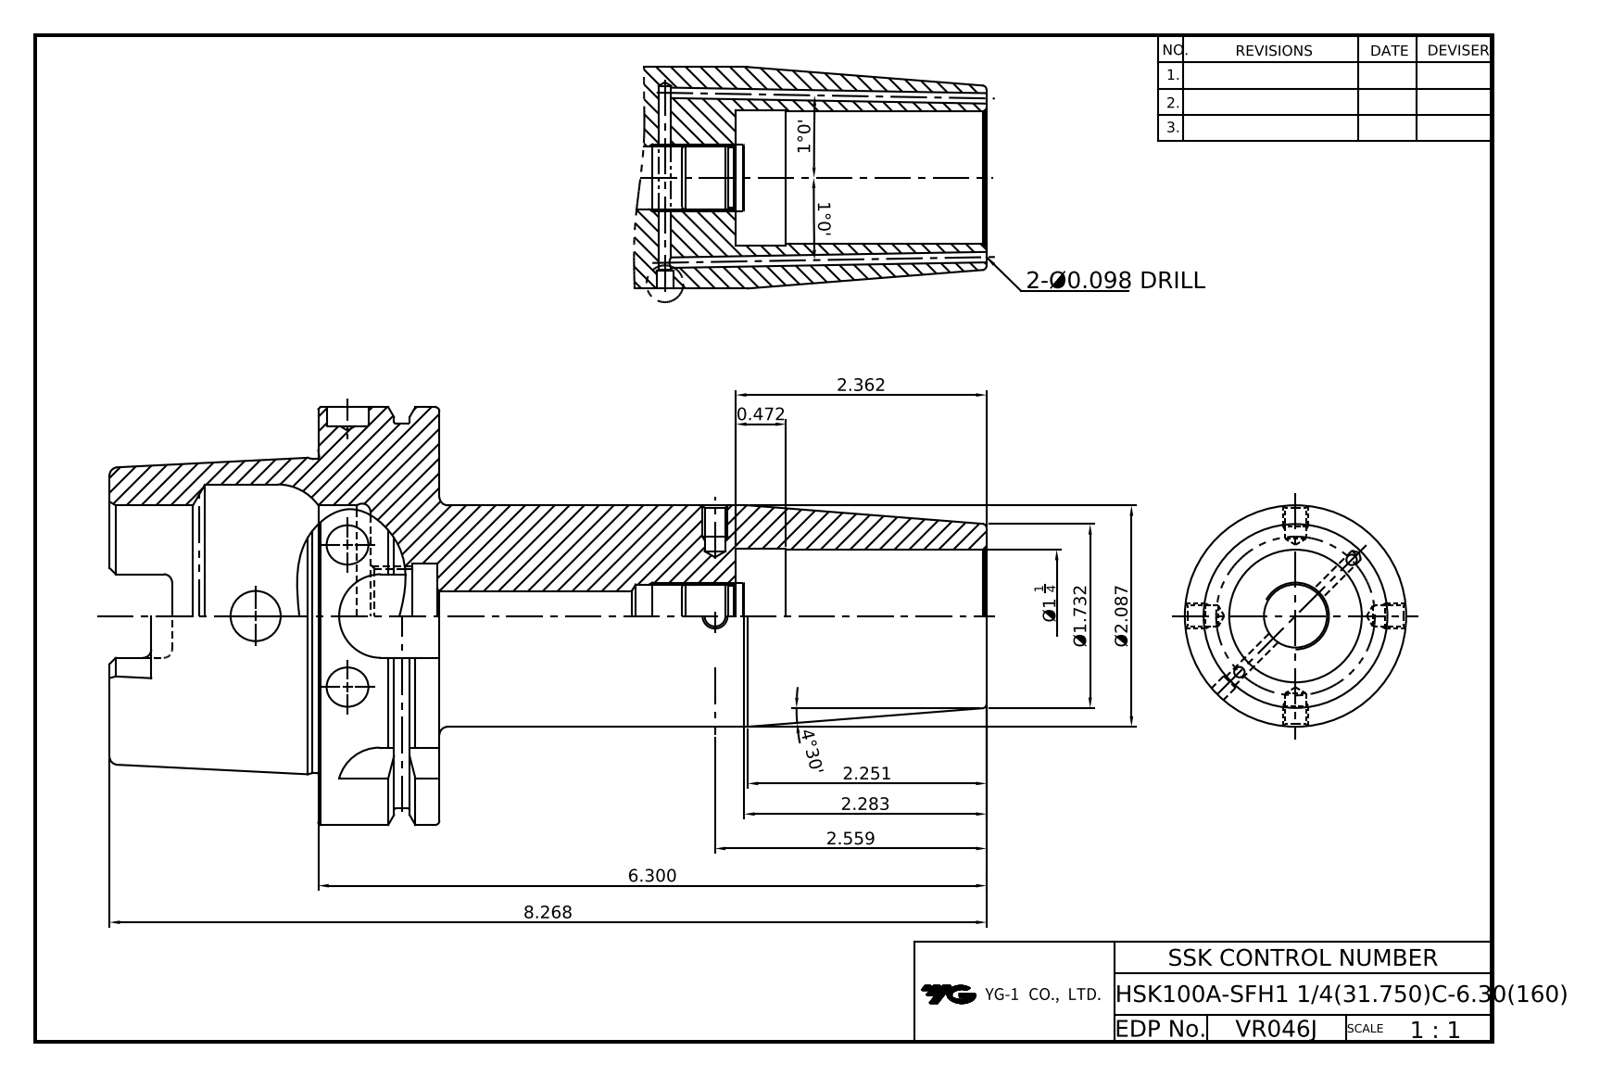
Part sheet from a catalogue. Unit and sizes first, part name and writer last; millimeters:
Units: millimetres
Overall size (bounding box): 210 × 100 × 100
Round holes (diameter × count): ⌀2.5 ×2, ⌀12 ×2, ⌀10 ×1, ⌀14.92 ×1, ⌀22.38 ×1, ⌀25 ×1, ⌀31.75 ×1, ⌀32.95 ×1, ⌀53 ×1, ⌀63 ×1
Round bosses / shafts (diameter × count): ⌀100 ×1, ⌀92 ×1, ⌀75.41 ×1
Partial cylindrical surfaces — rounded edges, fillets, slot ends (radius × count): R2 ×6, R4.88 ×4, R10 ×4
Main face-to-face distances: 29, 12.5, 16.5, 62.5, 50, 79, 150, 100, 87.5, 71
Volume: 464 516 mm³ · Surface area: 79 872 mm²
Bodies: 1 solid, 119 faces (38 planar, 37 cylindrical, 44 other)
Part name (STEP PRODUCT): LO-HSK100A-SFH31.75C-160
STEP written by: Autodesk Inventor 2022 (AUTOMOTIVE_DESIGN)
